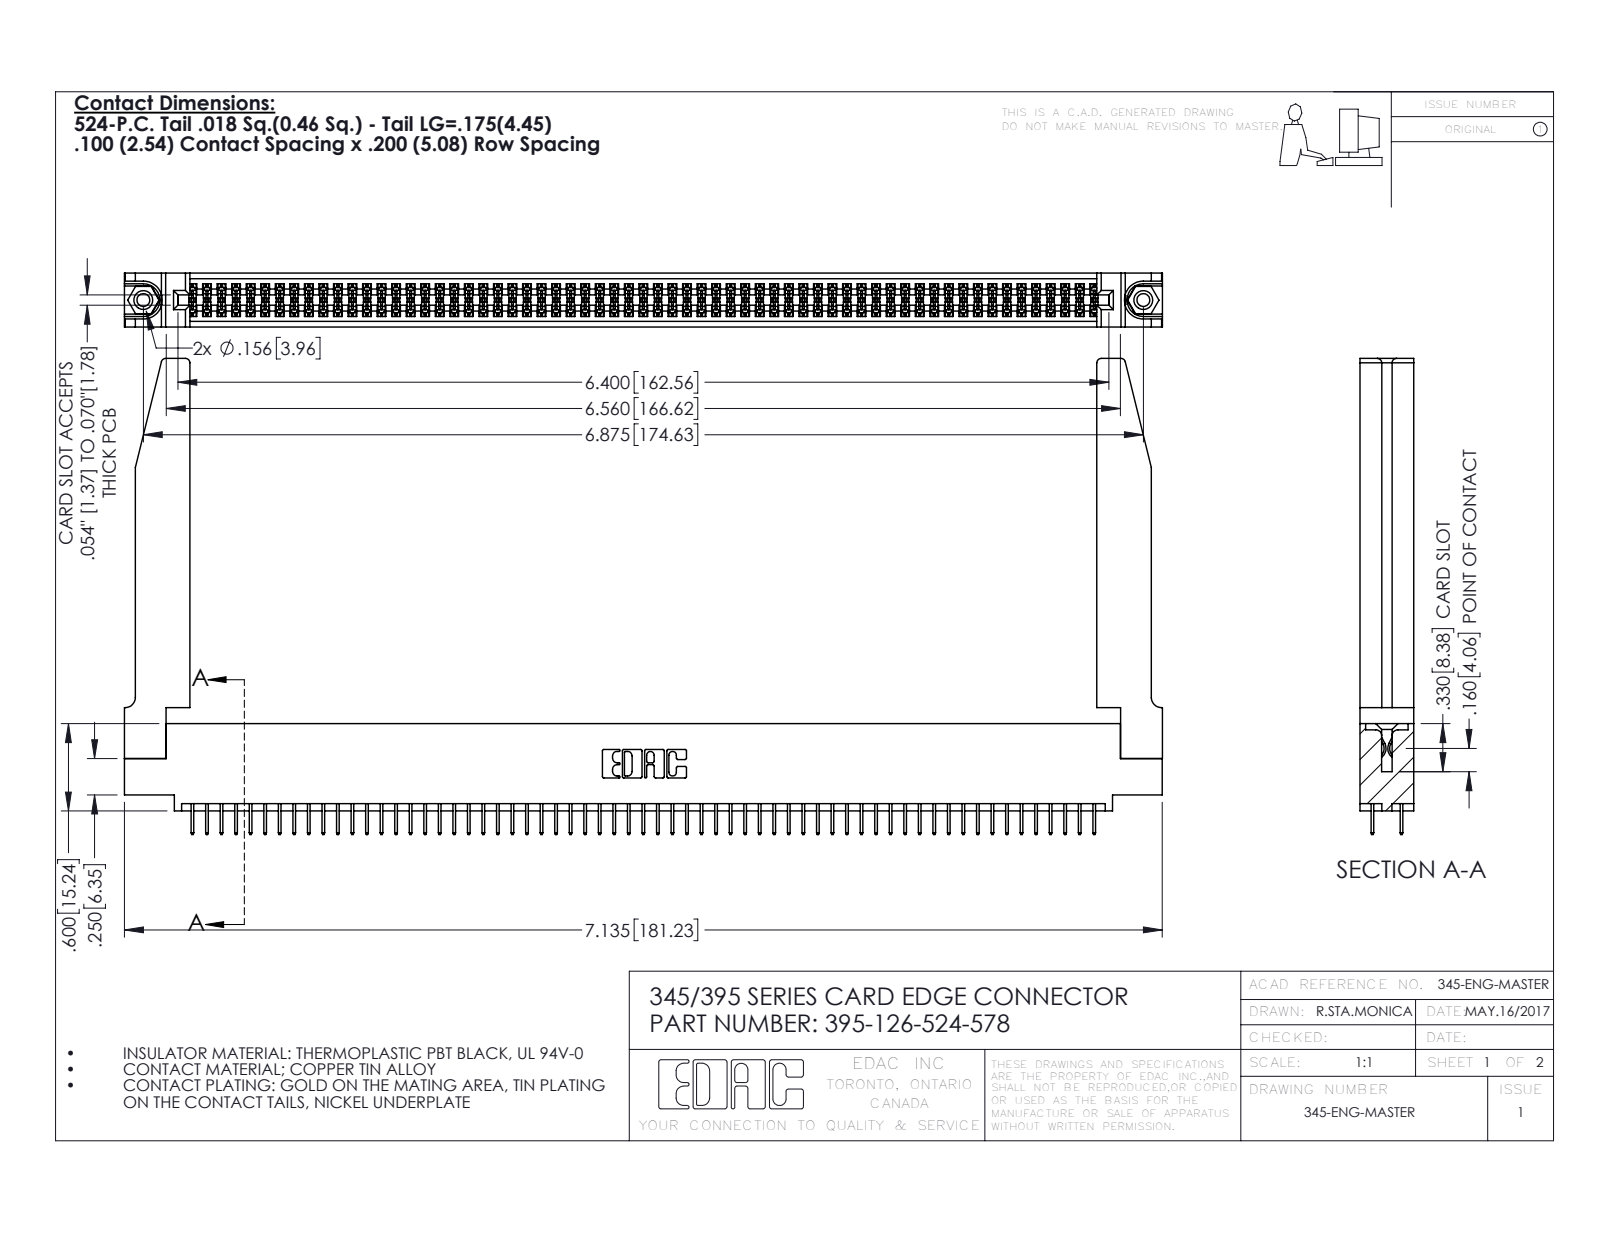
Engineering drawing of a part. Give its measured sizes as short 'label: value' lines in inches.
name: 345 Part_0.110 Offset - 0.156 Dia-TH; 345-292-001_345-293-124; 395-126-524-578; 345-250-001_345-250-001-102 (+1 more)
written by: SolidWorks 2016 (CONFIG_CONTROL_DESIGN)
unit: in
bodies: 131 solids, 7168 faces (5140 planar, 1976 cylindrical, 52 other)
size: 7.136 × 3.272 × 0.37
volume: 1.544 in³; area: 50.78 in²
holes: 2× ⌀0.089, 2× ⌀0.125, 2× ⌀0.156, 1× ⌀0.064
bosses: 2× ⌀0.155
rounds: 189× R0.006, 22× R0.01, 8× R0.03, 6× R0.007, 6× R0.031, 3× R0.026, 2× R0.014, 2× R0.019
face distances: 0.072, 0.37, 0.298, 0.2, 0.098, 0.272, 0.025, 0.225, 0.072, 0.175
hole spacings: 0.27, 6.639, 6.875
